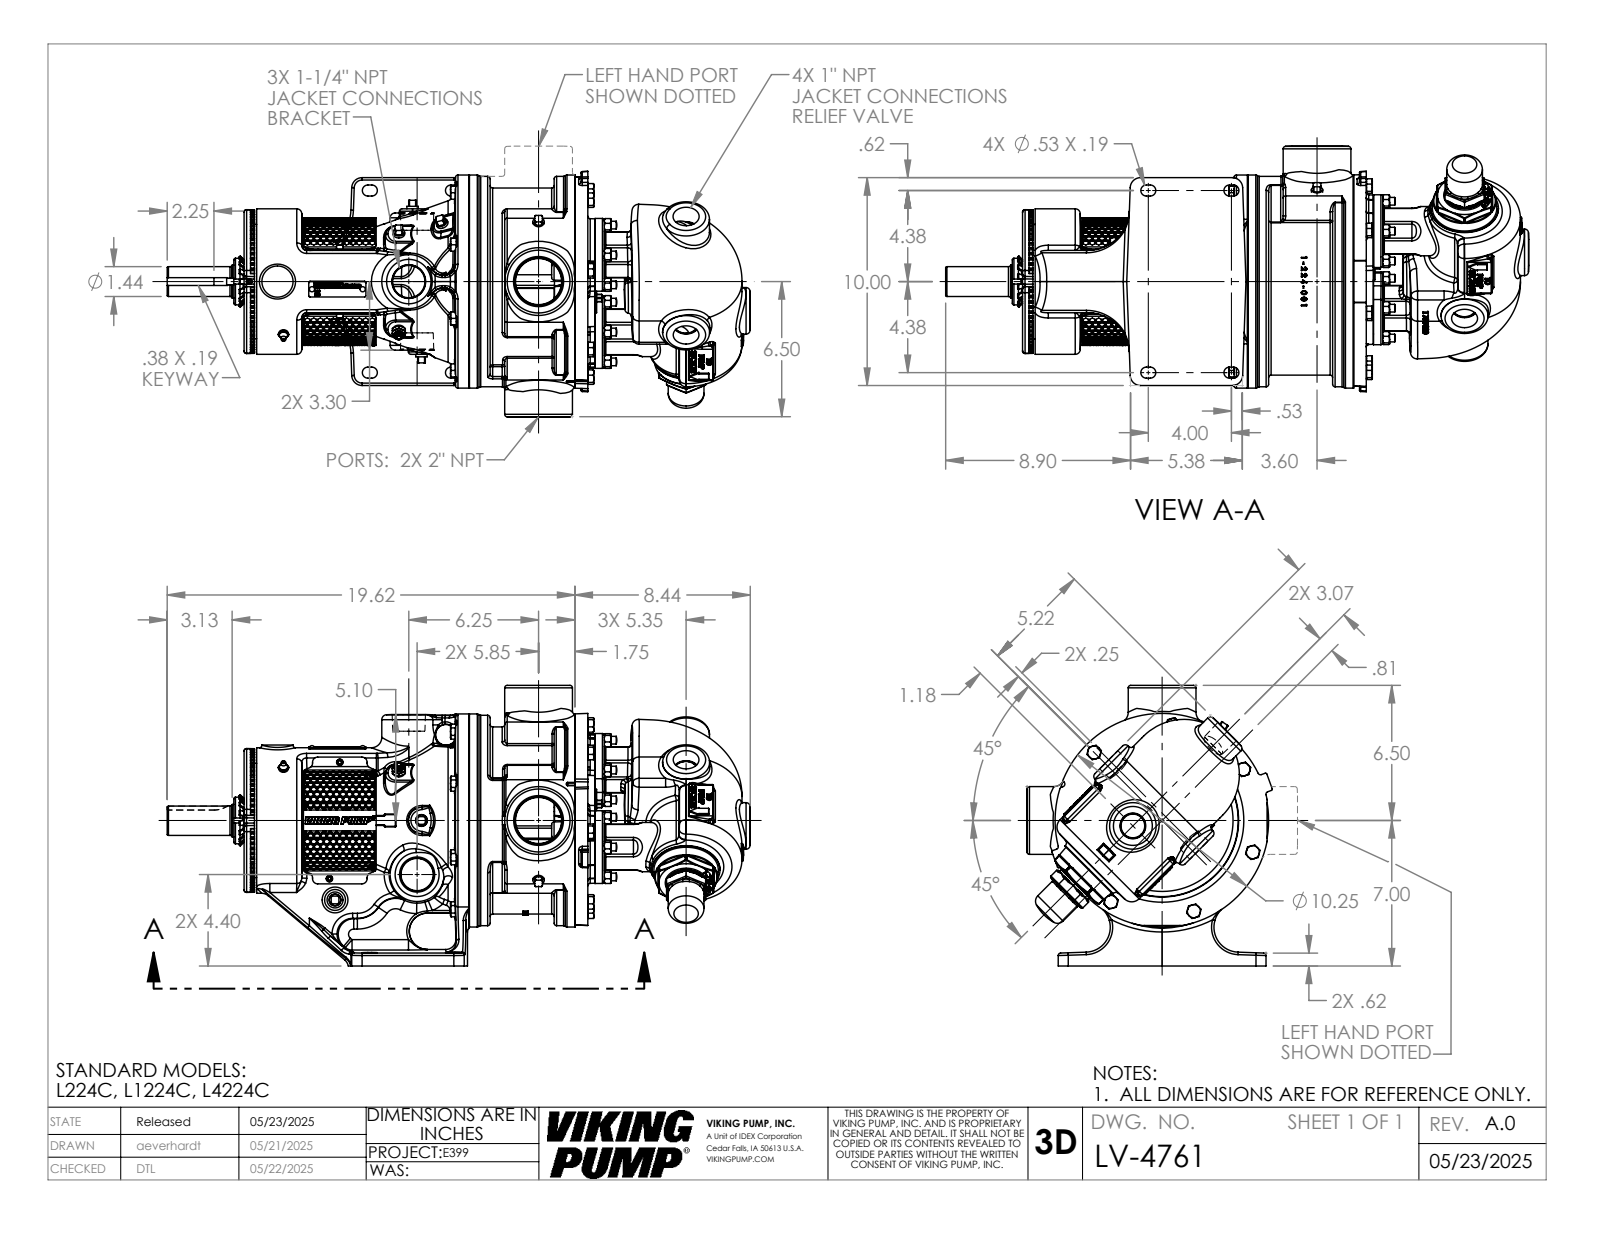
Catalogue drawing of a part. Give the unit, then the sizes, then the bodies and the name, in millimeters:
Units: millimetres
Overall size (bounding box): 712.7 × 342.9 × 300.2
Round holes (diameter × count): ⌀27.8 ×8, ⌀5.1 ×6, ⌀6.4 ×6, ⌀4 ×3, ⌀6.8 ×2, ⌀8 ×2, ⌀5.1 ×1, ⌀11.5 ×1, ⌀40.1 ×1, ⌀40.5 ×1, ⌀46.5 ×1, ⌀62 ×1
Round bosses / shafts (diameter × count): ⌀15.9 ×11, ⌀9.4 ×8, ⌀15.9 ×4, ⌀88.9 ×3, ⌀82.8 ×3, ⌀11.1 ×3, ⌀7.9 ×3, ⌀260.4 ×1
Partial cylindrical surfaces — rounded edges, fillets, slot ends (radius × count): R1.6 ×109, R3 ×90, R1.8 ×74, R0.8 ×36, R12.7 ×34, R6.1 ×16, R4.8 ×14, R1.5 ×13
Main face-to-face distances: 350.3, 89.8, 260.5, 57.2, 12.7, 54.4, 144.3, 404.7, 15.4, 69.9
Hole centre spacings: 76.2, 34.9, 55.4, 91.7, 112.9, 117.5, 162.7, 166.1
Volume: 17 530 000 mm³ · Surface area: 910 300 mm²
Bodies: 1 solid, 5228 faces (1658 planar, 888 cylindrical, 2682 other)
Part name (STEP PRODUCT): LV-4761
STEP written by: SolidWorks 2024 (AUTOMOTIVE_DESIGN)
